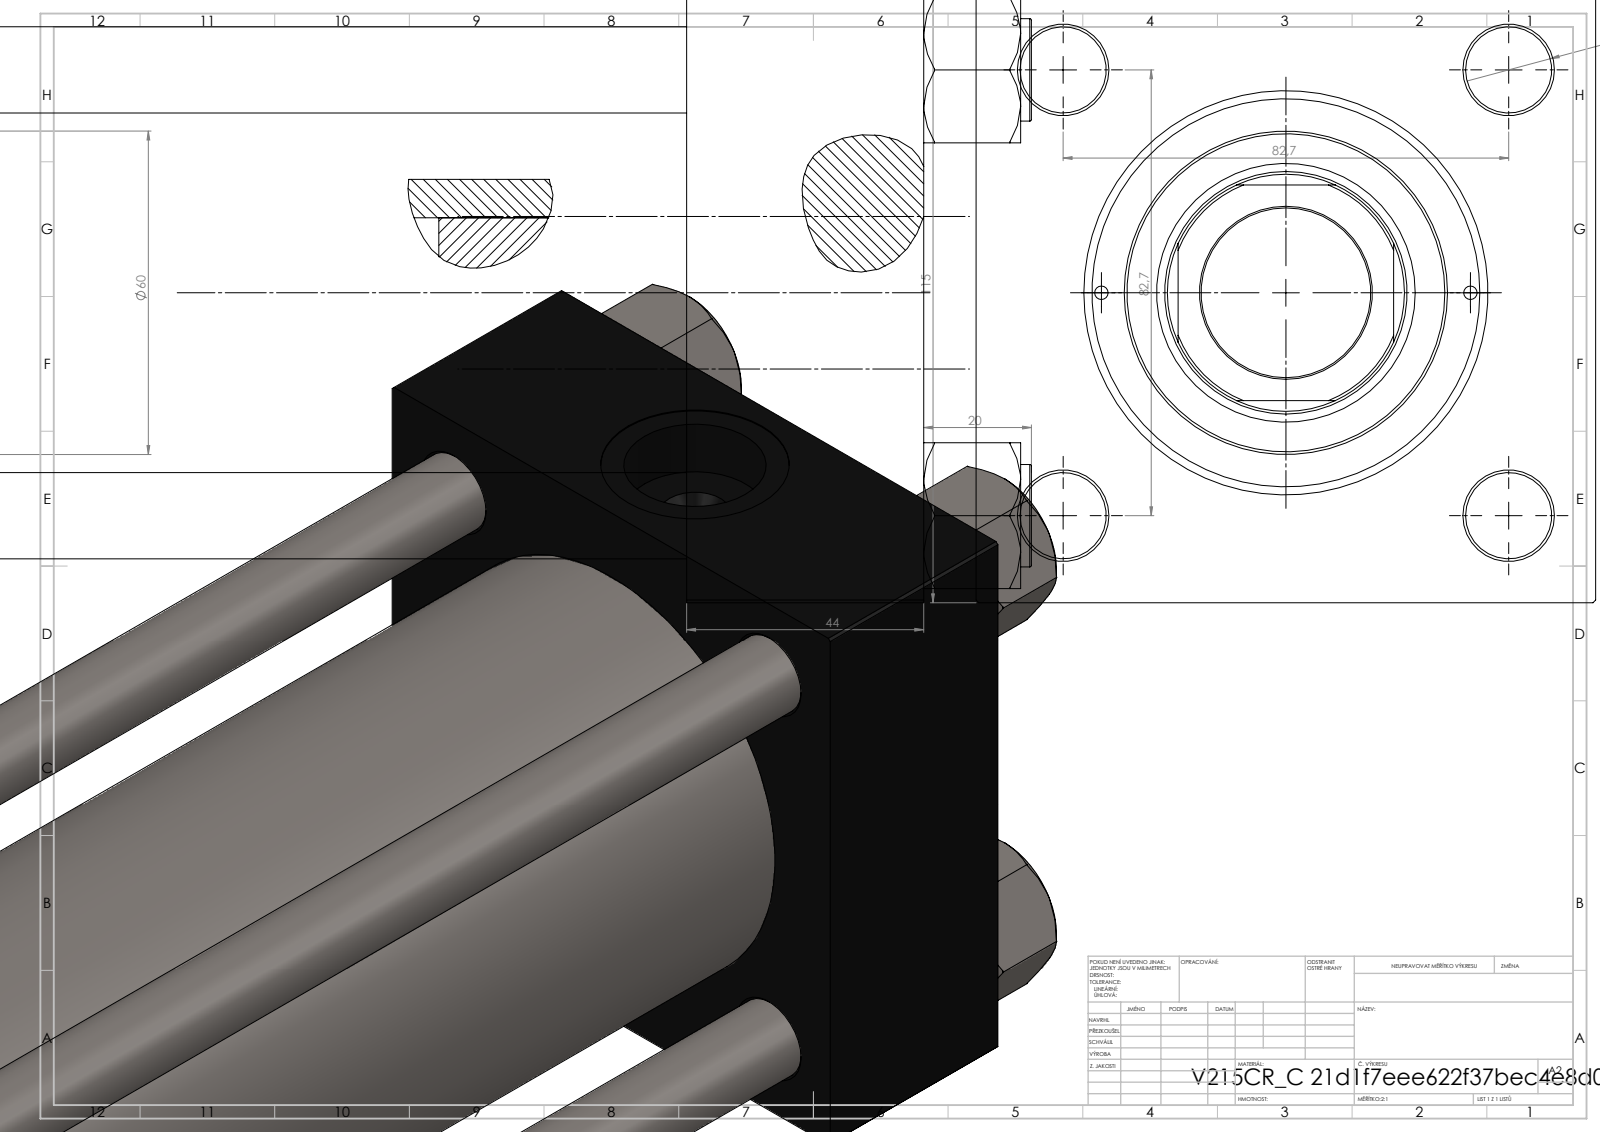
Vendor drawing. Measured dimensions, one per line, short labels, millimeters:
name: V215CR_C_Body; V215CR_C_TYCINKA; V215_VC_A; NUT_M5_C (+1 more)
written by: SolidWorks 2019 (CONFIG_CONTROL_DESIGN)
unit: mm
bodies: 11 solids, 1203 faces (576 planar, 91 cylindrical, 536 other)
size: 560 × 115 × 115
volume: 2 868 000 mm³; area: 559 063 mm²
holes: 4× ⌀16, 2× ⌀2.5, 2× ⌀7, 2× ⌀26.44, 2× ⌀35, 1× ⌀31.5, 1× ⌀45, 1× ⌀48, 1× ⌀61, 1× ⌀72, 1× ⌀80
bosses: 4× ⌀19, 1× ⌀86, 1× ⌀60
rounds: 1× R22
face distances: 115, 44, 509, 465, 440, 396, 69, 480.3, 436.3, 40.3
hole spacings: 41.96, 58.48, 82.7, 86.17, 34.25, 116.96, 68.5, 441
